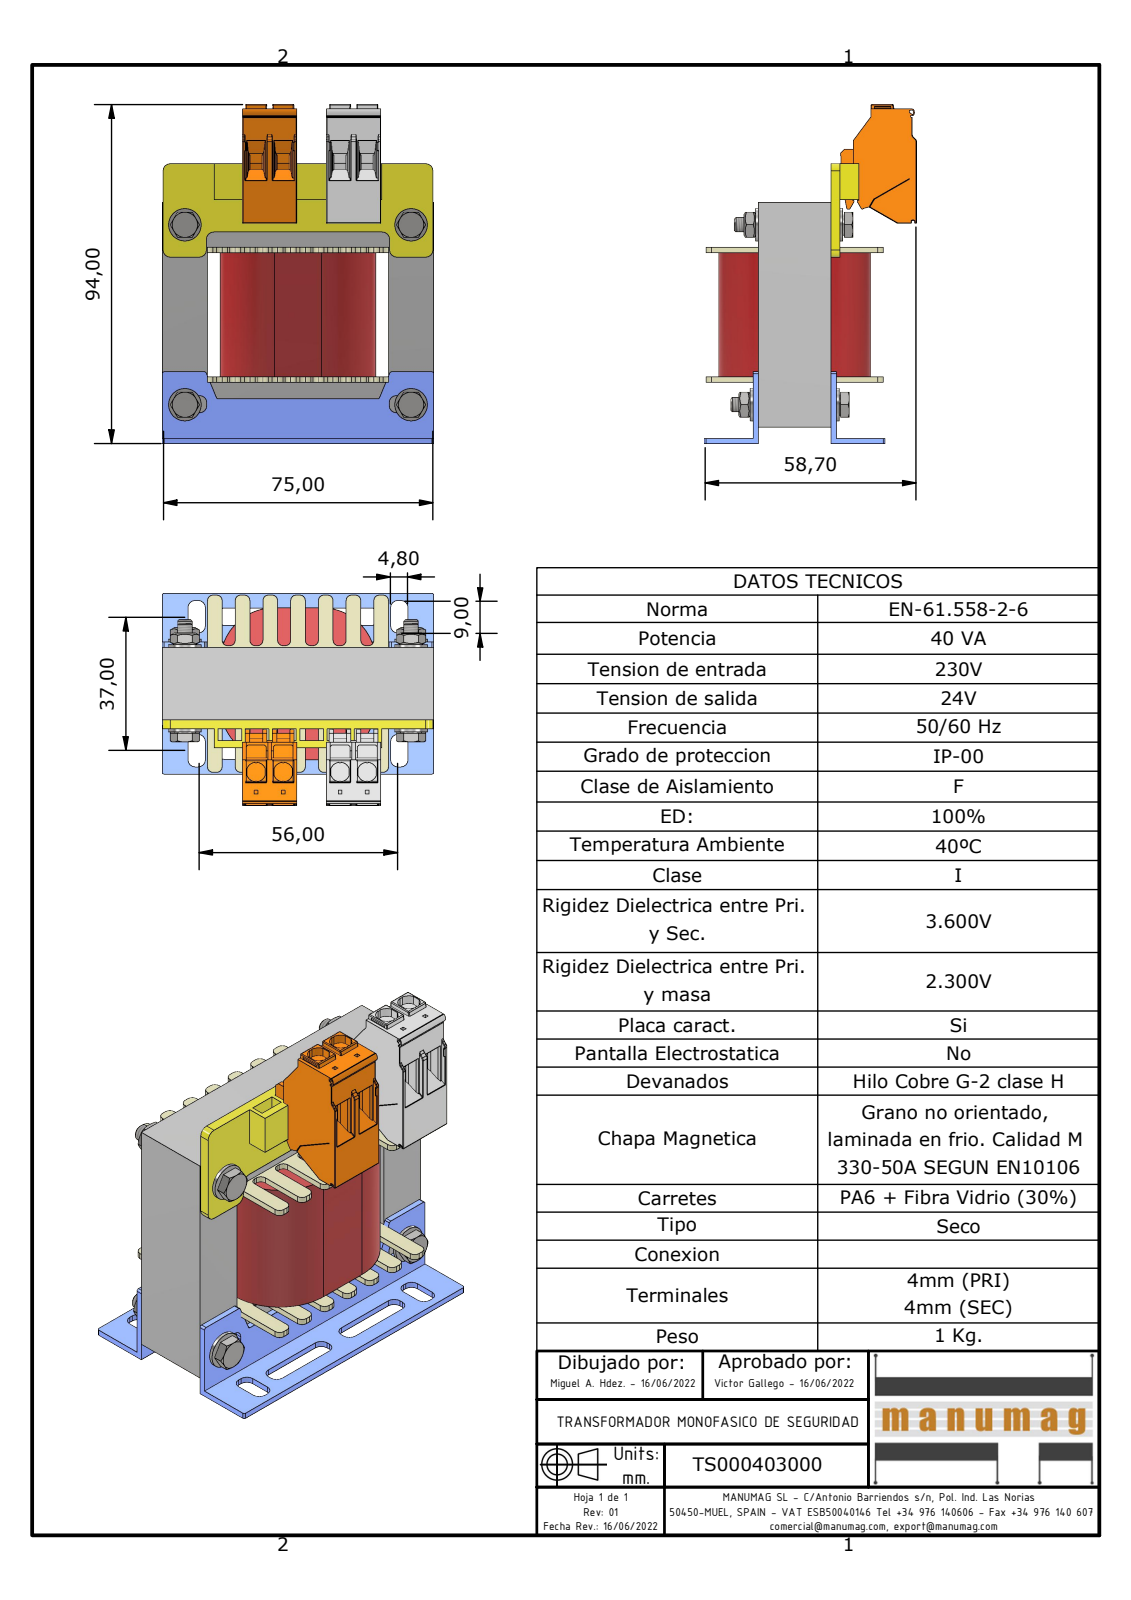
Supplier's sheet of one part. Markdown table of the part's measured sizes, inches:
| quantity | value |
| --- | --- |
| part name | TS000403000; EI75 x 62,5 - 20 (RC25); AF25DIN; EI 75 X 62,5 - 20 (+6 more) |
| STEP written by | Autodesk Inventor 2022 (AUTOMOTIVE_DESIGN) |
| units | inches |
| bodies | 23 solids, 3870 faces (3060 planar, 576 cylindrical, 234 other) |
| overall size | 3.715 × 2.953 × 2.311 |
| volume | 8.451 in³ |
| surface area | 94.43 in² |
| round holes (diameter × count) | 0.128 × 4, 0.169 × 4, 0.177 × 4, 0.157 × 2 |
| round bosses / shafts (diameter × count) | 0.354 × 4, 0.232 × 4, 0.143 × 4, 0.157 × 2 |
| partial cylindrical surfaces (radius × count) | 0.006 × 160, 0.059 × 52, 0.008 × 48, 0.079 × 48, 0.02 × 22, 0.012 × 7, 0.039 × 4, 0.106 × 4 |
| main face-to-face distances | 0.492, 1.969, 0.787, 0.059, 0.984, 1.476, 2.461, 0.673, 2.091, 0.846 |
| hole center spacings | 1.969, 2.461, 3.151 |
